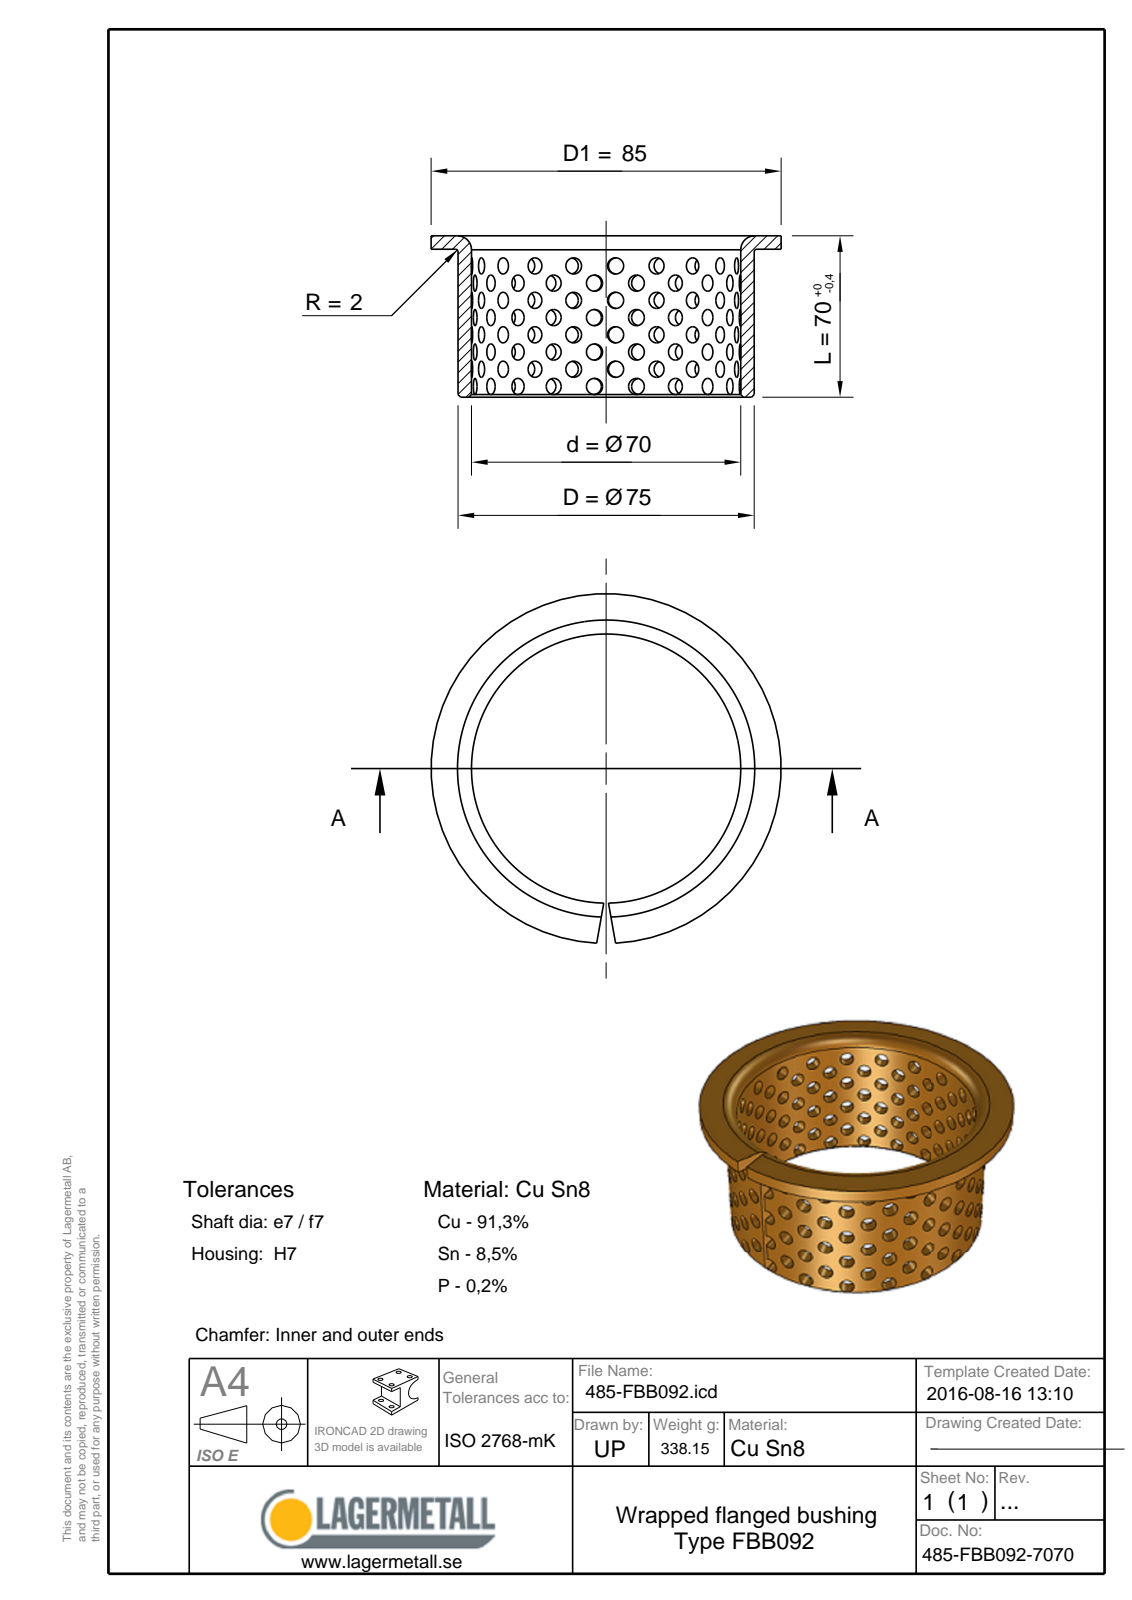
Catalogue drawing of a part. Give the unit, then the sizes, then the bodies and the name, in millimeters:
Units: millimetres
Overall size (bounding box): 85 × 84.96 × 70
Round holes (diameter × count): ⌀70 ×1
Round bosses / shafts (diameter × count): ⌀85 ×1, ⌀75 ×1
Main face-to-face distances: 2.5, 67.5, 70
Volume: 41 747 mm³ · Surface area: 34 920 mm²
Bodies: 1 solid, 12 faces (5 planar, 3 cylindrical, 4 other)
Part name (STEP PRODUCT): 485-FBB092-7070
STEP written by: Spatial InterOp 3D (CONFIG_CONTROL_DESIGN)
